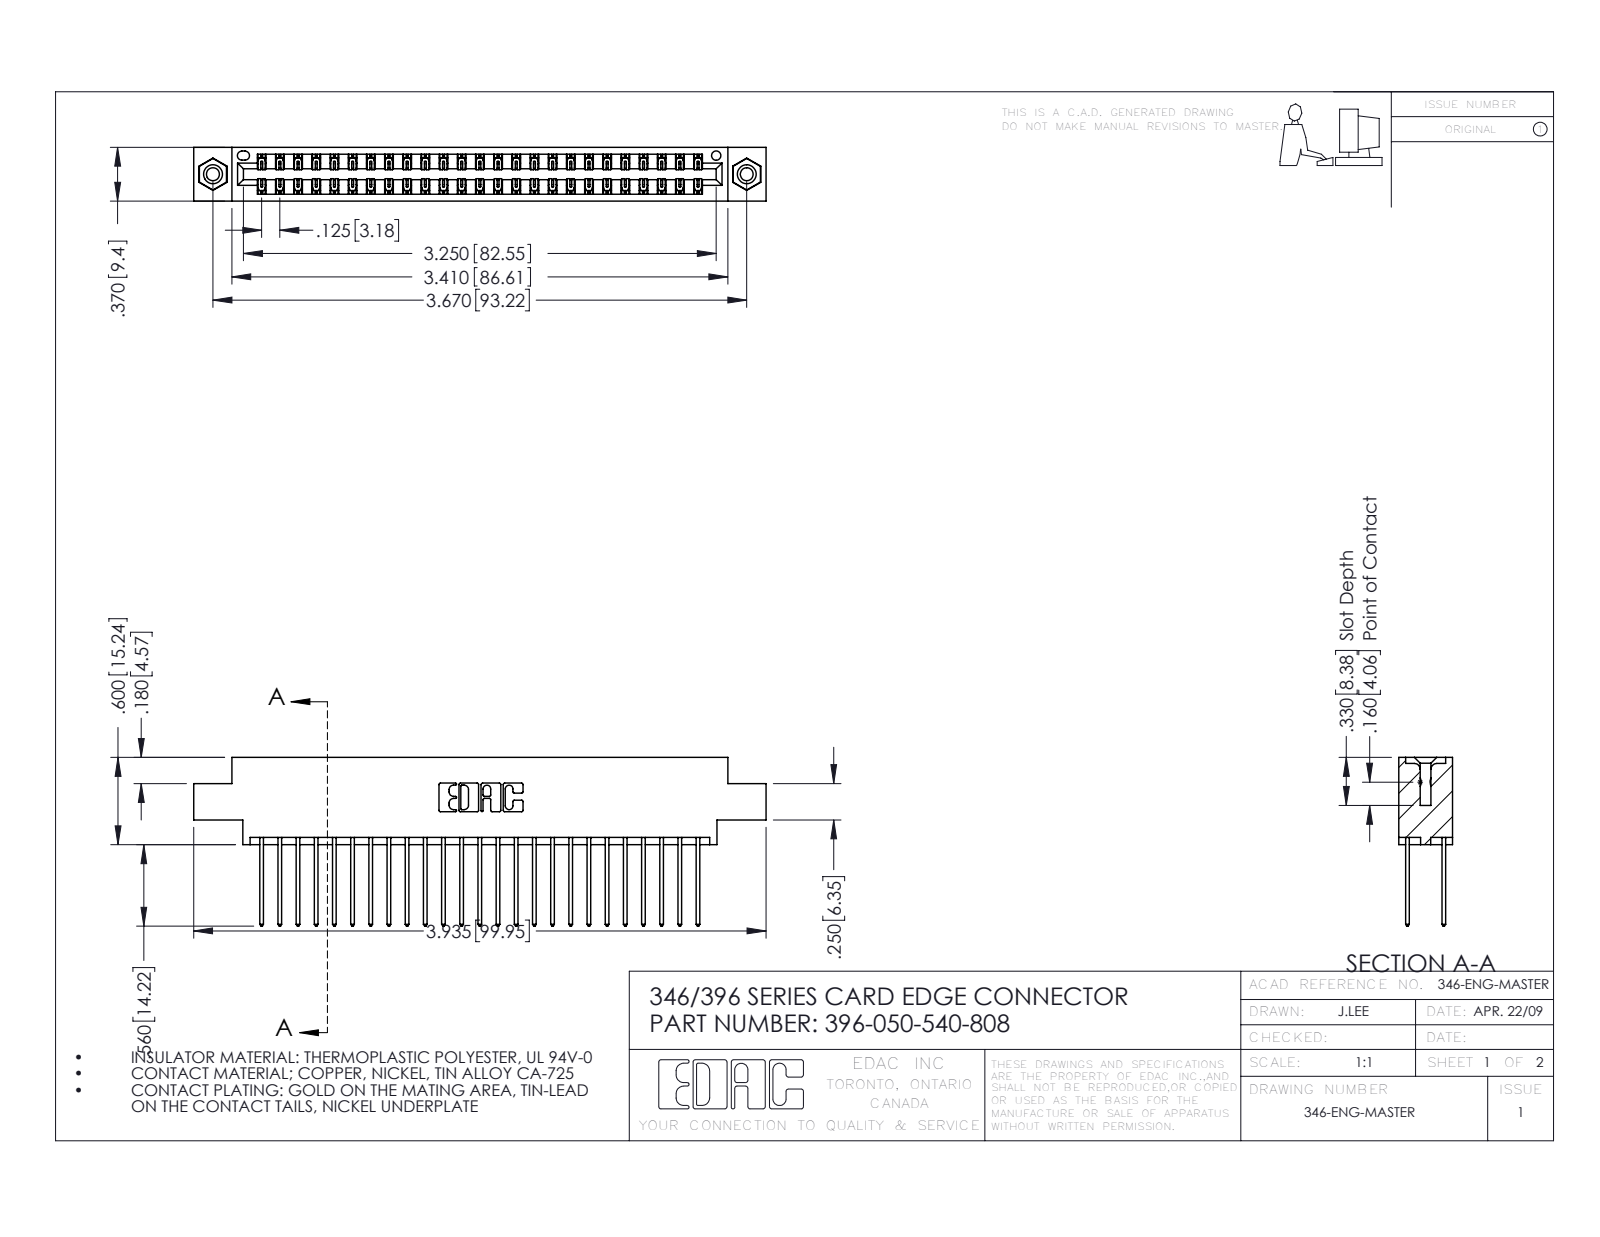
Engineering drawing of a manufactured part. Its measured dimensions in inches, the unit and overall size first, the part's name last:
Units: inches
Overall size (bounding box): 3.935 × 1.16 × 0.37
Round holes (diameter × count): ⌀0.089 ×2, ⌀0.125 ×2, ⌀0.156 ×2, ⌀0.064 ×1
Round bosses / shafts (diameter × count): ⌀0.155 ×2
Partial cylindrical surfaces — rounded edges, fillets, slot ends (radius × count): R0.006 ×75, R0.01 ×50, R0.01 ×22, R0.007 ×6, R0.031 ×6, R0.026 ×3, R0.014 ×2, R0.022 ×2
Main face-to-face distances: 0.048, 0.322, 0.25, 0.37, 0.072, 0.298, 0.025, 0.275, 0.222, 0.148
Hole centre spacings: 0.246, 3.462, 3.67
Volume: 0.588 in³ · Surface area: 21.83 in²
Bodies: 53 solids, 2786 faces (1862 planar, 908 cylindrical, 16 other)
Part name (STEP PRODUCT): 346 Part_0.170 Offset - 0.156 Dia-TI; 345-250-001_345-250-003-102; 396-050-540-808; 345-292-001_345-293-140
STEP written by: SolidWorks 2016 (CONFIG_CONTROL_DESIGN)
